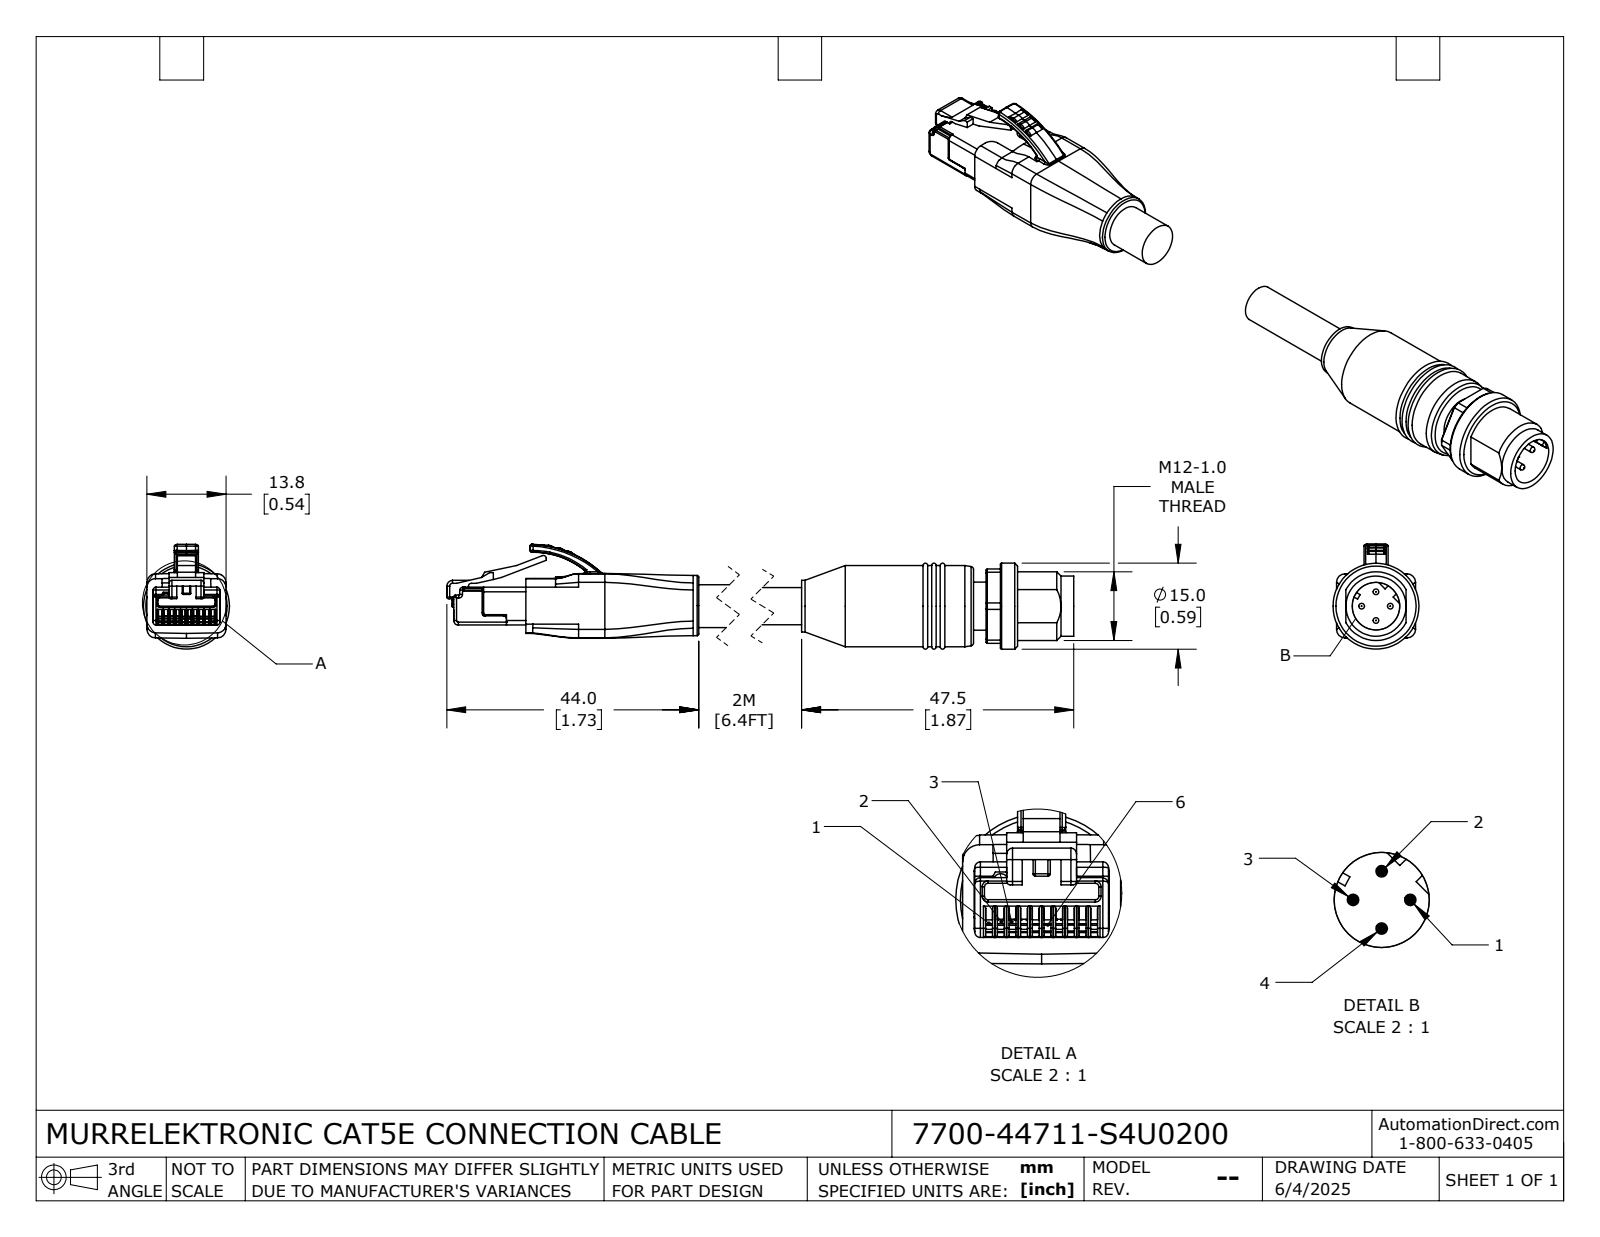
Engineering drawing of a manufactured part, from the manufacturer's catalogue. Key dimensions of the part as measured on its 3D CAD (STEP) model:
Part name (STEP PRODUCT): 7700-44711-S4U0200; 7700-44711-S4U0200_MALE; 7700-44711-S4U0200_RJ45
STEP written by: SolidWorks 2024 (CONFIG_CONTROL_DESIGN)
Units: millimetres
Bodies: 2 solids, 757 faces (357 planar, 235 cylindrical, 165 other)
Overall size (bounding box): 144.5 × 18.29 × 15
Volume: 11 873 mm³ · Surface area: 5 775 mm²
Round holes (diameter × count): ⌀8.3 ×1
Round bosses / shafts (diameter × count): ⌀1 ×4, ⌀10.5 ×2, ⌀15 ×1, ⌀14.2 ×1, ⌀9 ×1, ⌀8.4 ×1, ⌀7.5 ×1, ⌀6.5 ×1
Partial cylindrical surfaces — rounded edges, fillets, slot ends (radius × count): R0.2 ×61, R0.5 ×25, R0.3 ×14, R1.5 ×9, R0.8 ×5, R0.54 ×2, R5 ×2, R0.13 ×1
Main face-to-face distances: 13.8, 2.2, 1.65, 12.15, 1.01, 12.79, 0.64, 11.14, 9.8, 0.9
